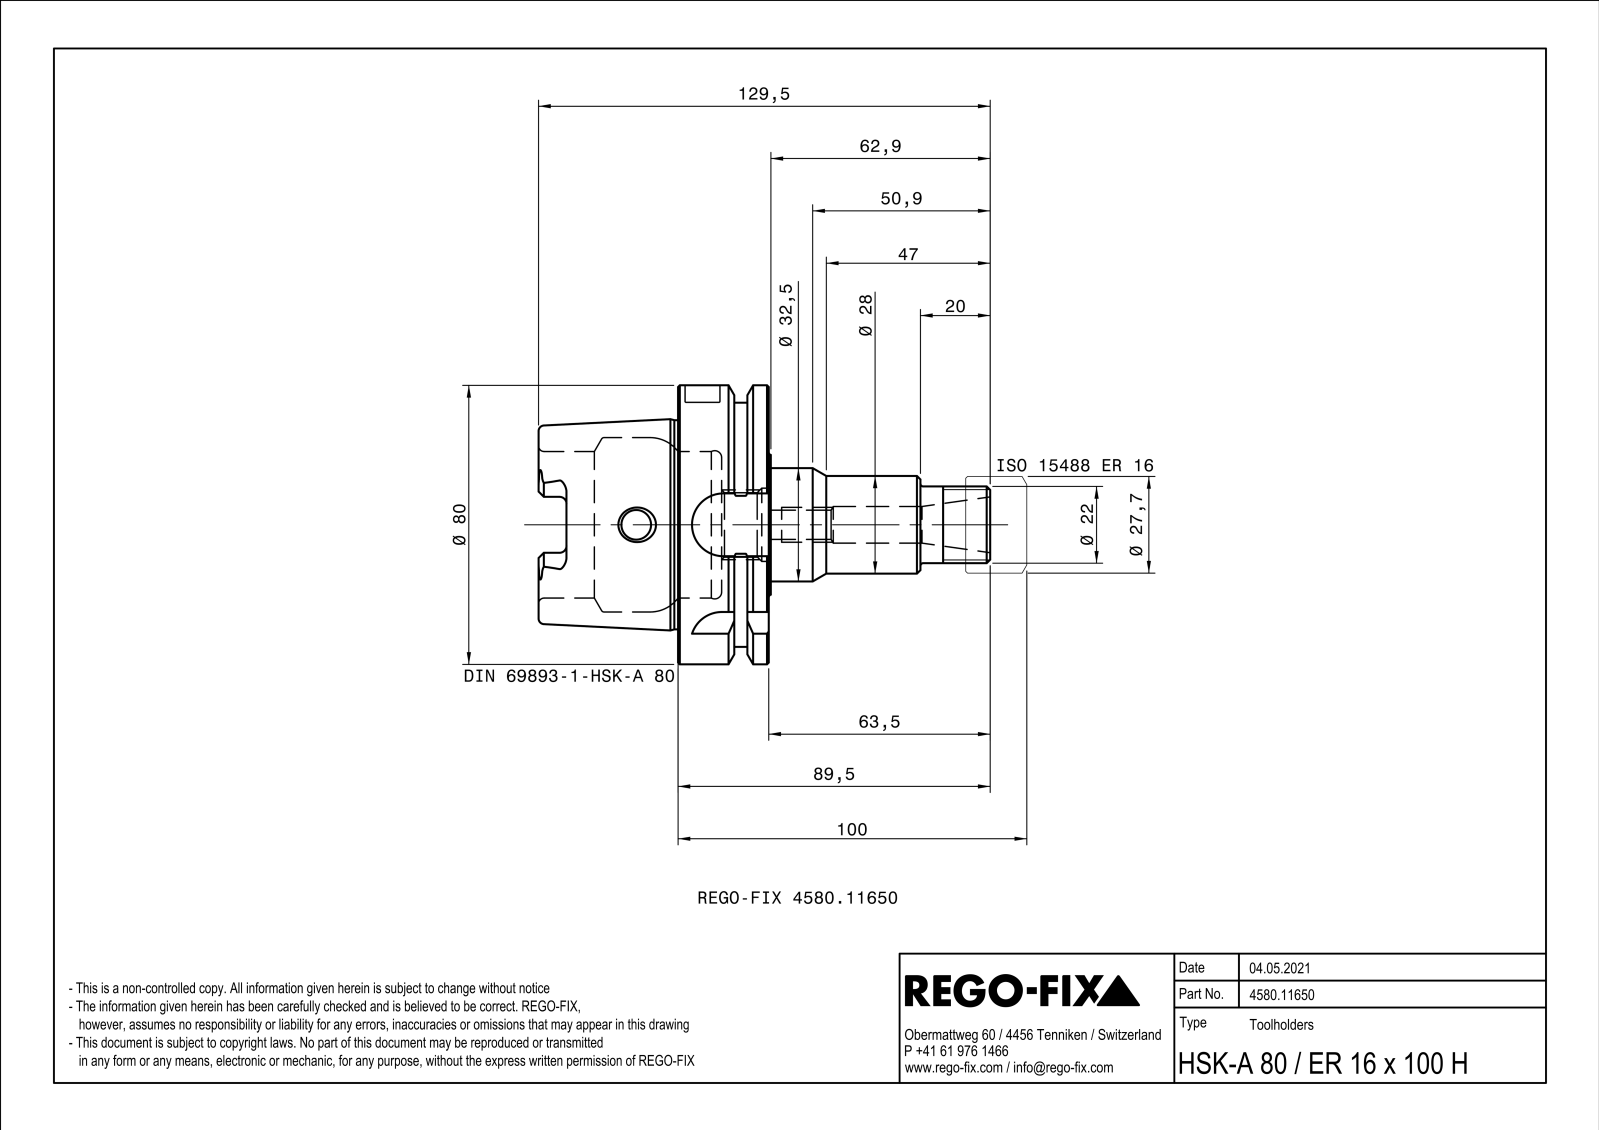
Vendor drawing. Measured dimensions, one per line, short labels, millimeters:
name: NOCUT
written by: SIEMENS PLM Software Solid Edge ST10 (AUTOMOTIVE_DESIGN)
unit: mm
bodies: 2 solids, 309 faces (95 planar, 84 cylindrical, 130 other)
size: 129.7 × 80.3 × 80.3
volume: 341 343 mm³; area: 82 826 mm²
holes: 4× ⌀4, 2× ⌀8.5, 1× ⌀8.38, 1× ⌀10, 1× ⌀10.2, 1× ⌀10.5, 1× ⌀18.38, 1× ⌀21, 1× ⌀41.7, 1× ⌀42, 1× ⌀50
bosses: 1× ⌀80.3, 1× ⌀80, 1× ⌀70, 1× ⌀60.42, 1× ⌀59.98, 1× ⌀32.8, 1× ⌀32.5, 1× ⌀28.3
rounds: 10× R2, 4× R3.88, 4× R4.18, 4× R9
face distances: 12.5, 26, 26.2, 66, 40, 39.8, 13.5, 12.7, 52.5, 13.7
hole spacings: 25, 4.36, 28.68, 32.14
